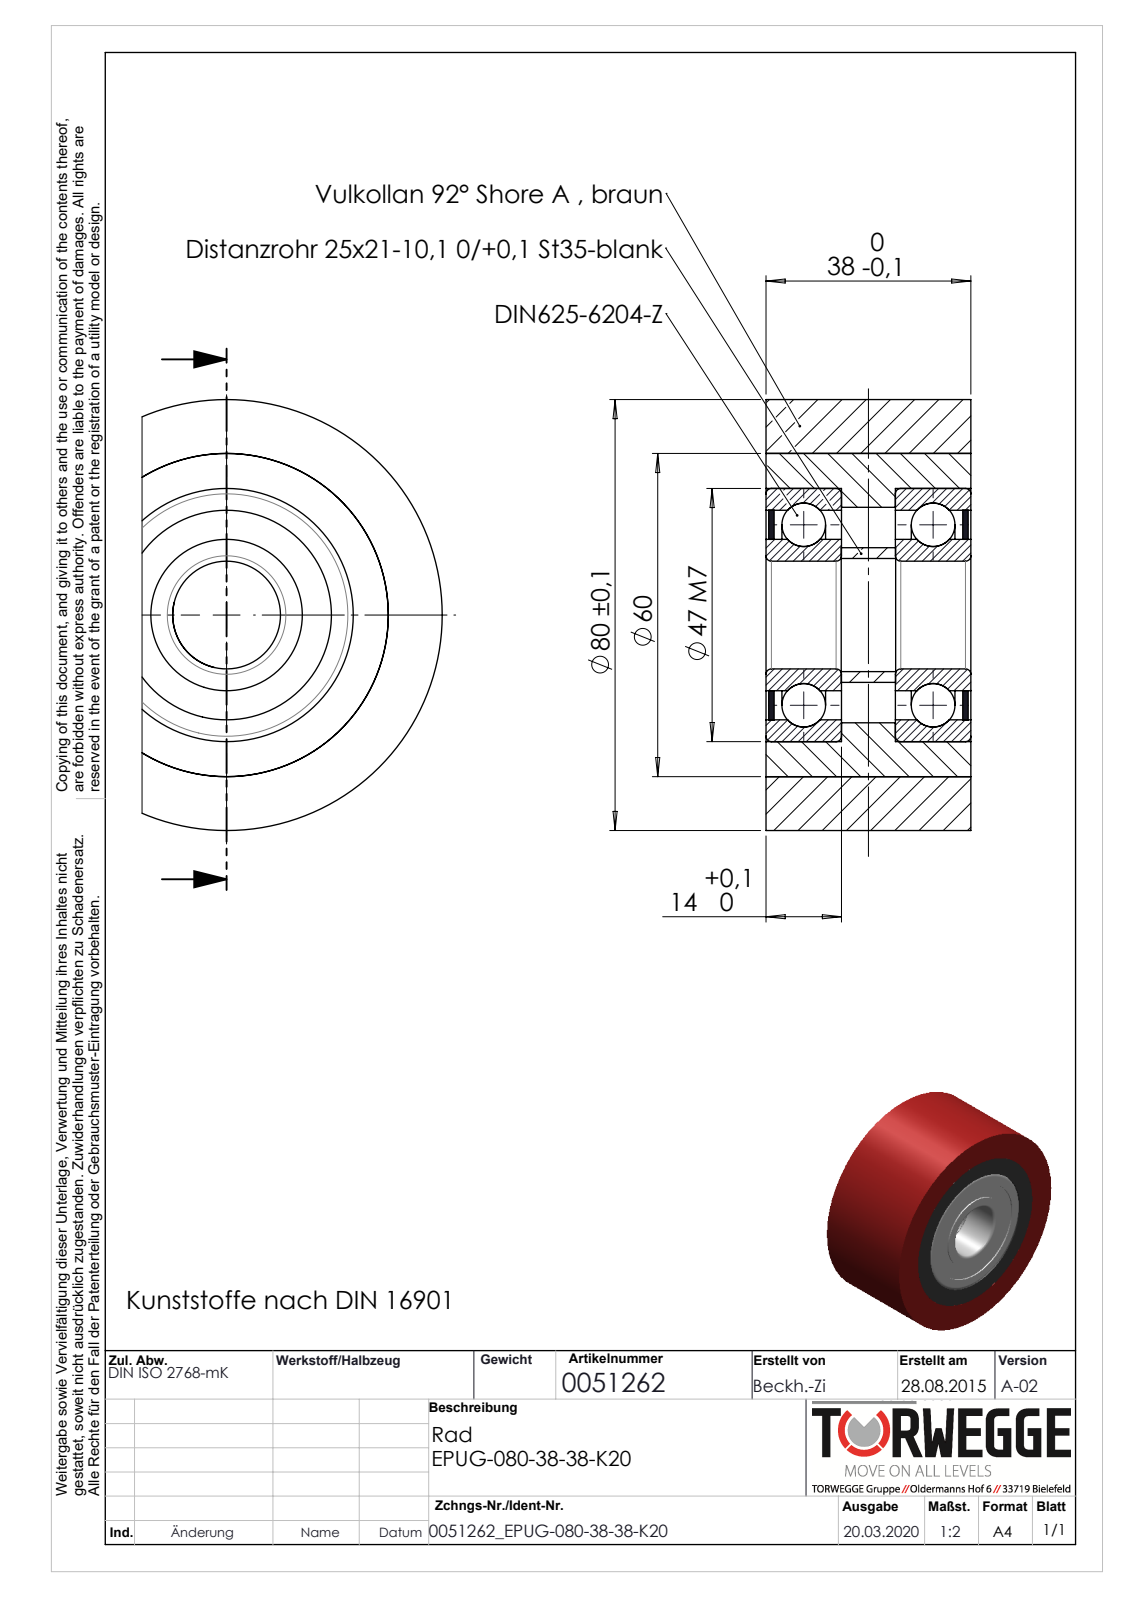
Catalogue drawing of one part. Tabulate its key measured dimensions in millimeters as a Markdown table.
| quantity | value |
| --- | --- |
| part name | 0051262 |
| STEP written by | SolidWorks 2018 (AUTOMOTIVE_DESIGN) |
| units | millimeters |
| bodies | 11 solids, 108 faces (24 planar, 56 cylindrical, 28 other) |
| overall size | 80 × 80 × 38 |
| volume | 154 980 mm³ |
| surface area | 59 098 mm² |
| round holes (diameter × count) | 20 × 1, 21 × 1, 28.1 × 1, 38.9 × 1, 40 × 1, 47 × 1, 60 × 1 |
| round bosses / shafts (diameter × count) | 80 × 1, 25 × 1 |
| main face-to-face distances | 24, 38, 12, 0.5, 1.5, 12.5, 13.5, 1, 14, 13 |
